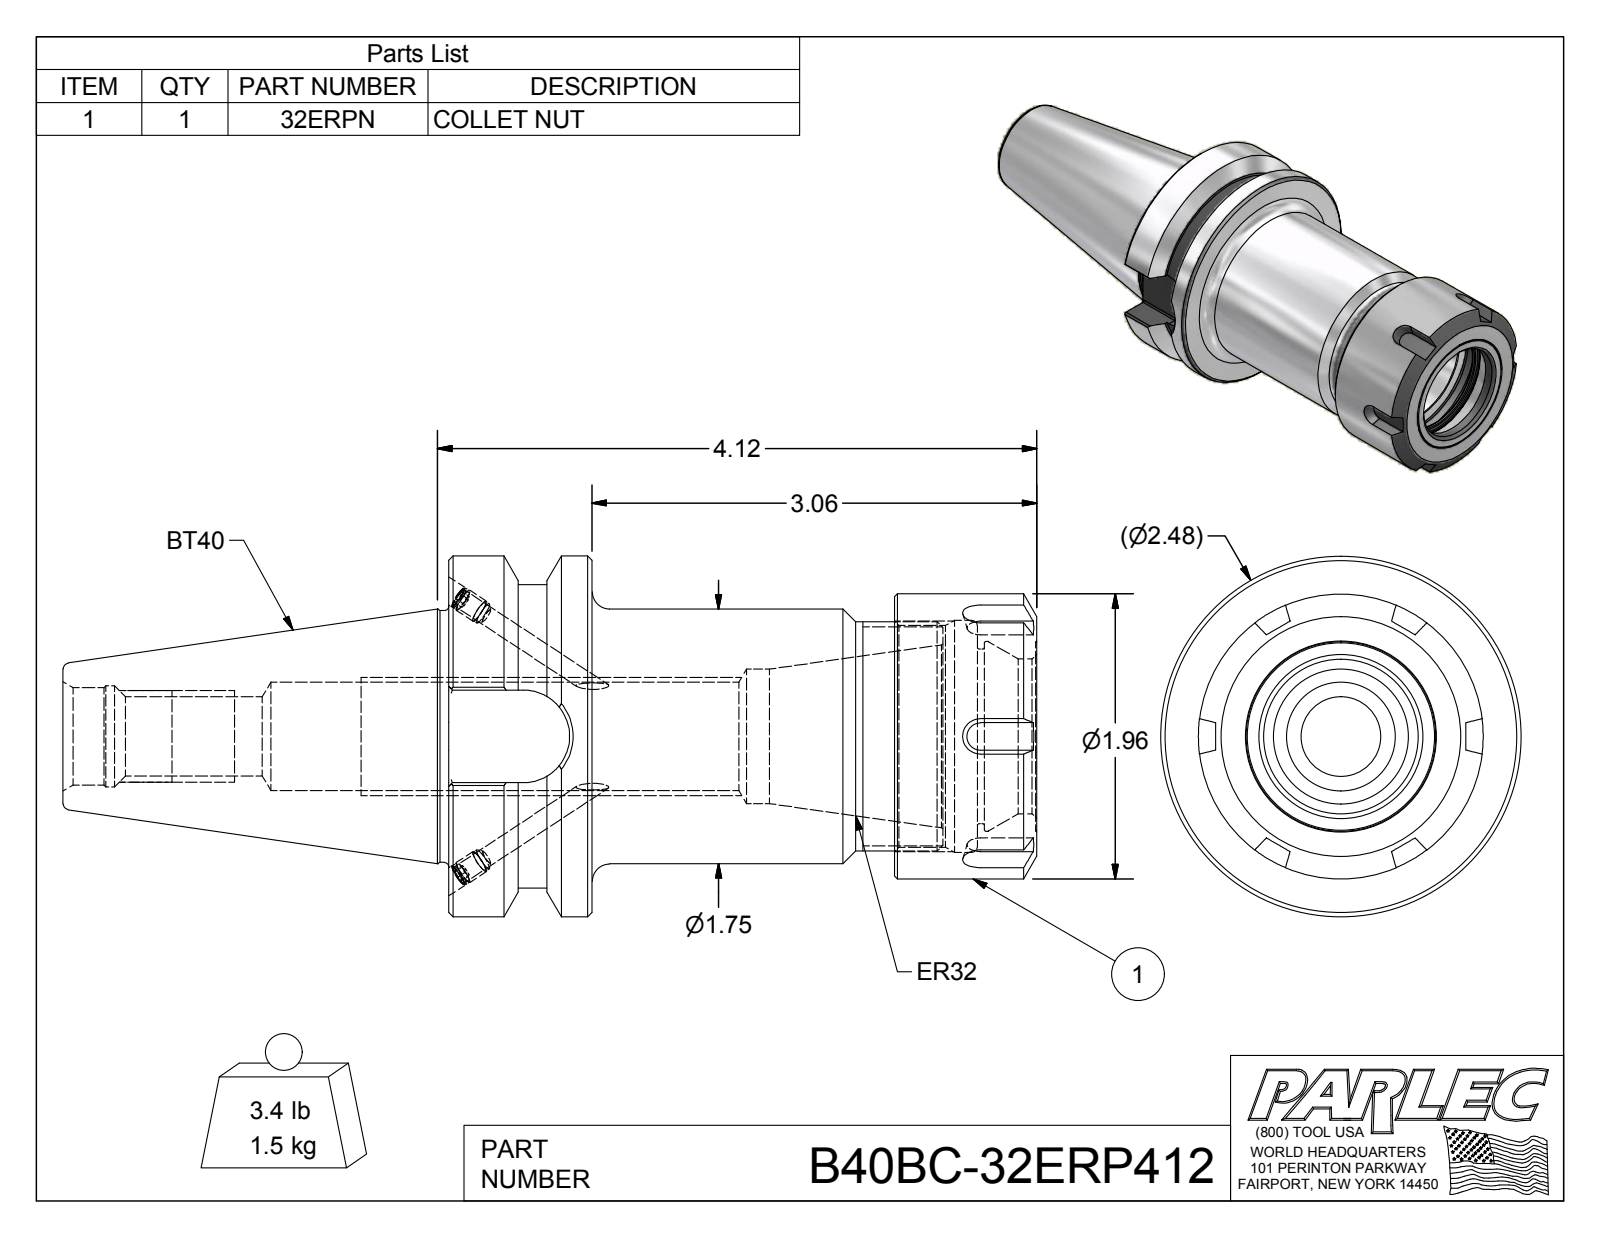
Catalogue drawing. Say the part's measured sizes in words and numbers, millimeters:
The part is named "B40BC-32ERP412; B40BCB-32ER4-1; 029-965; 32ERPN". Its 3-D file was written by "Autodesk Inventor 2012 (AUTOMOTIVE_DESIGN)". It is 4 solids with 157 faces: 68 planar, 39 cylindrical and 50 other. Overall it measures 170.1 by 63 by 63 millimeters. Its volume is 196 000 cubic millimeters and its surface area 45 350 square millimeters. Round holes: 2 of diameter 3.3, 2 of diameter 4.1, 1 of diameter 13.8, 1 of diameter 17, 1 of diameter 17.6, 1 of diameter 18.9, 1 of diameter 23.5, 1 of diameter 27, 1 of diameter 30.5, 1 of diameter 33.1, 1 of diameter 38.7, 1 of diameter 40.5. Round bosses or shafts: 2 of diameter 4.2, 2 of diameter 4, 1 of diameter 63, 1 of diameter 53, 1 of diameter 49.7, 1 of diameter 44.5, 1 of diameter 43.9, 1 of diameter 40. Partial cylindrical surfaces (rounded edges, fillets, slot ends): 8 of radius 0.5, 1 of radius 8.1. The main face-to-face distances are 25, 102.7, 77.7, 77.8, 52.8, 24.8, 92.3, 67.3, 14.5, 10.3.
